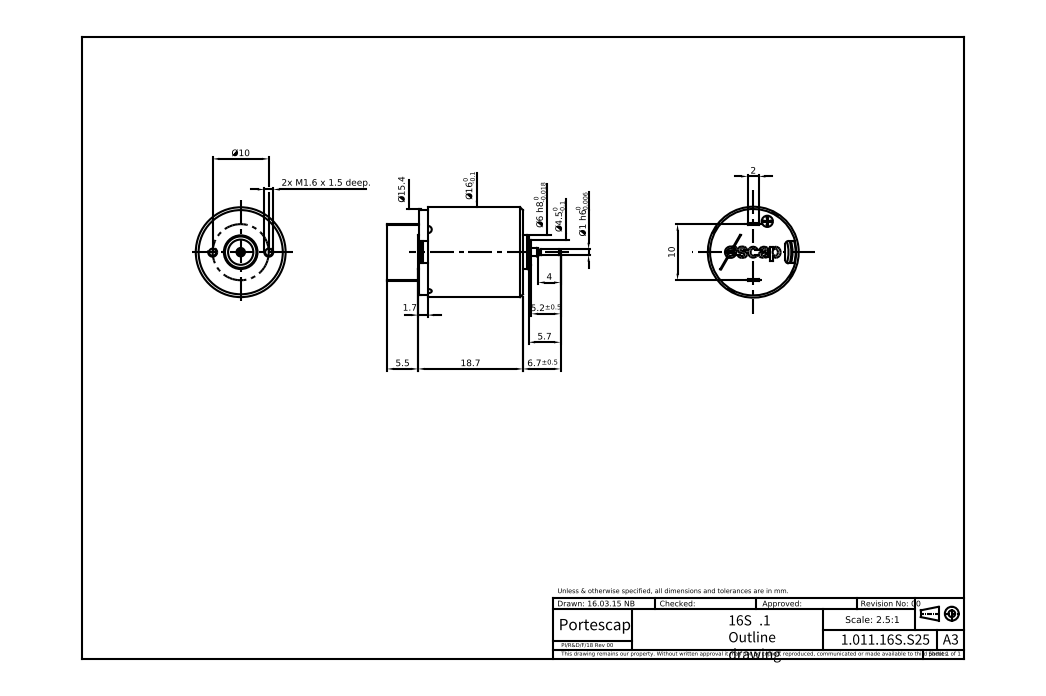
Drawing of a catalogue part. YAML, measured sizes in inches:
part_name: "1101162101_16S78_ASM"
step_written_by: "PRO/ENGINEER BY PARAMETRIC TECHNOLOGY CORPORATION, 2014310 (CONFIG_CONTROL_DESIGN)"
units: inches
bodies: {solids: 1, faces: 527, planar: 359, cylindrical: 104, other: 64}
overall_size: [1.217, 0.63, 0.63]
volume: 0.222
surface_area: 3.286
round_holes:
  - {diameter: 0.049, count: 2}
  - {diameter: 0.06, count: 1}
  - {diameter: 0.071, count: 1}
  - {diameter: 0.079, count: 1}
  - {diameter: 0.087, count: 1}
  - {diameter: 0.098, count: 1}
  - {diameter: 0.197, count: 1}
  - {diameter: 0.606, count: 1}
  - {diameter: 0.614, count: 1}
round_bosses_or_shafts:
  - {diameter: 0.63, count: 1}
  - {diameter: 0.602, count: 1}
  - {diameter: 0.594, count: 1}
  - {diameter: 0.425, count: 1}
  - {diameter: 0.236, count: 1}
  - {diameter: 0.177, count: 1}
  - {diameter: 0.142, count: 1}
  - {diameter: 0.11, count: 1}
partial_cylinders:
  - {radius: 0.01, count: 10}
  - {radius: 0.004, count: 5}
  - {radius: 0.039, count: 5}
  - {radius: 0.075, count: 3}
  - {radius: 0.02, count: 2}
  - {radius: 0.021, count: 2}
  - {radius: 0.024, count: 2}
  - {radius: 0.03, count: 2}
face_to_face_distances: [0.736, 0.02, 0.717, 0.063, 0.673, 0.043, 0.039, 0.028, 0.024, 0.697]
hole_center_spacings: [0.197, 0.247, 0.1, 0.112, 0.12, 0.128, 0.132, 0.15]
